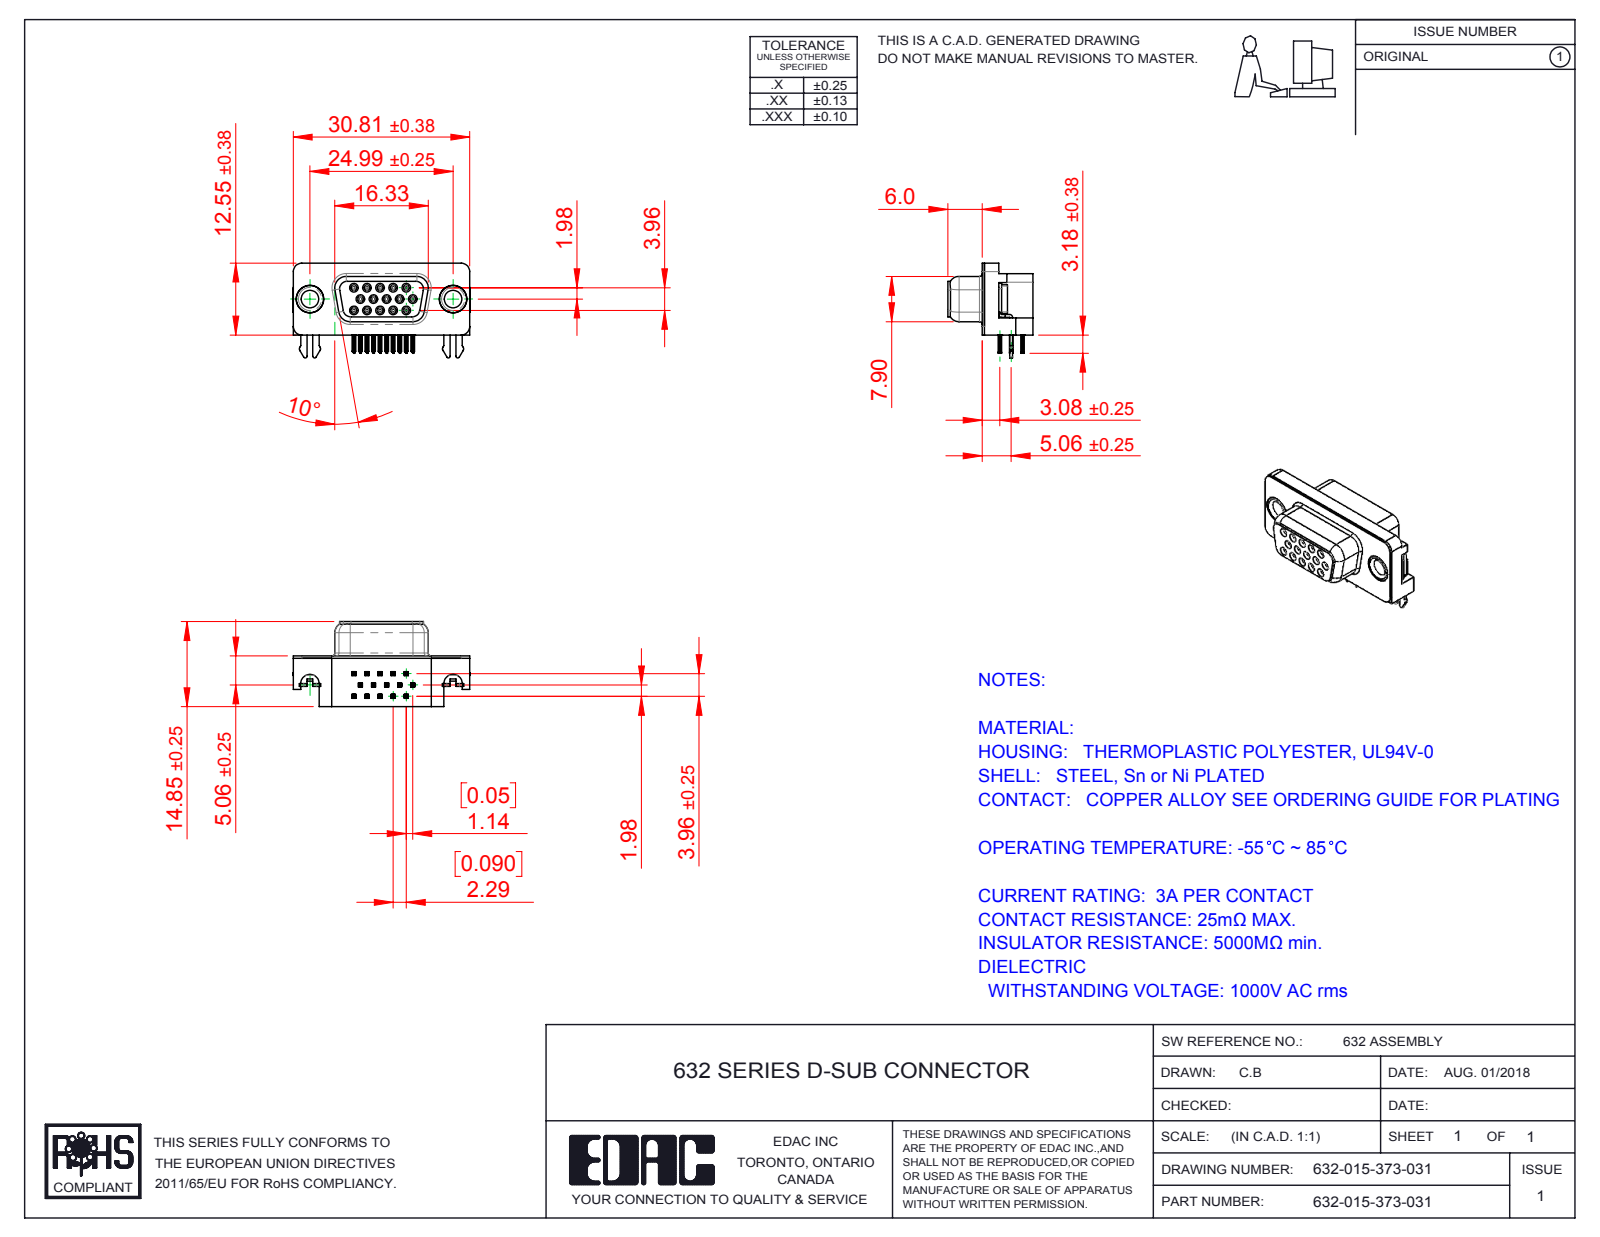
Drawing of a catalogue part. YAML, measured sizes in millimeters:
part_name: "632 Shell_9 Socket; 632 Thru Hole Rivet; 632 Contact Middle_Recessed; 632 2 Prong Board Lock (+5 more)"
step_written_by: "SolidWorks 2016 (CONFIG_CONTROL_DESIGN)"
units: millimeters
bodies: {solids: 21, faces: 2298, planar: 990, cylindrical: 594, other: 714}
overall_size: [30.89, 16.55, 14.85]
volume: 2907
surface_area: 4991
round_holes:
  - {diameter: 0.8, count: 15}
  - {diameter: 0.9, count: 15}
  - {diameter: 3.05, count: 2}
  - {diameter: 4, count: 2}
  - {diameter: 4.8, count: 2}
  - {diameter: 5, count: 2}
round_bosses_or_shafts:
  - {diameter: 1.2, count: 15}
  - {diameter: 4.9, count: 2}
  - {diameter: 4.75, count: 2}
  - {diameter: 3.85, count: 2}
partial_cylinders:
  - {radius: 0.1, count: 120}
  - {radius: 0.15, count: 60}
  - {radius: 0.35, count: 30}
  - {radius: 0.34, count: 15}
  - {radius: 1, count: 11}
  - {radius: 0.28, count: 10}
  - {radius: 0.5, count: 10}
  - {radius: 0.25, count: 8}
face_to_face_distances: [0.4, 1.98, 8.45, 8.85, 2.9, 2.5, 5.95, 6.4, 6.7, 7.05]
hole_center_spacings: [2.28, 2.29, 3.96, 4.57, 6.05, 3.97, 4.58, 6.86]
